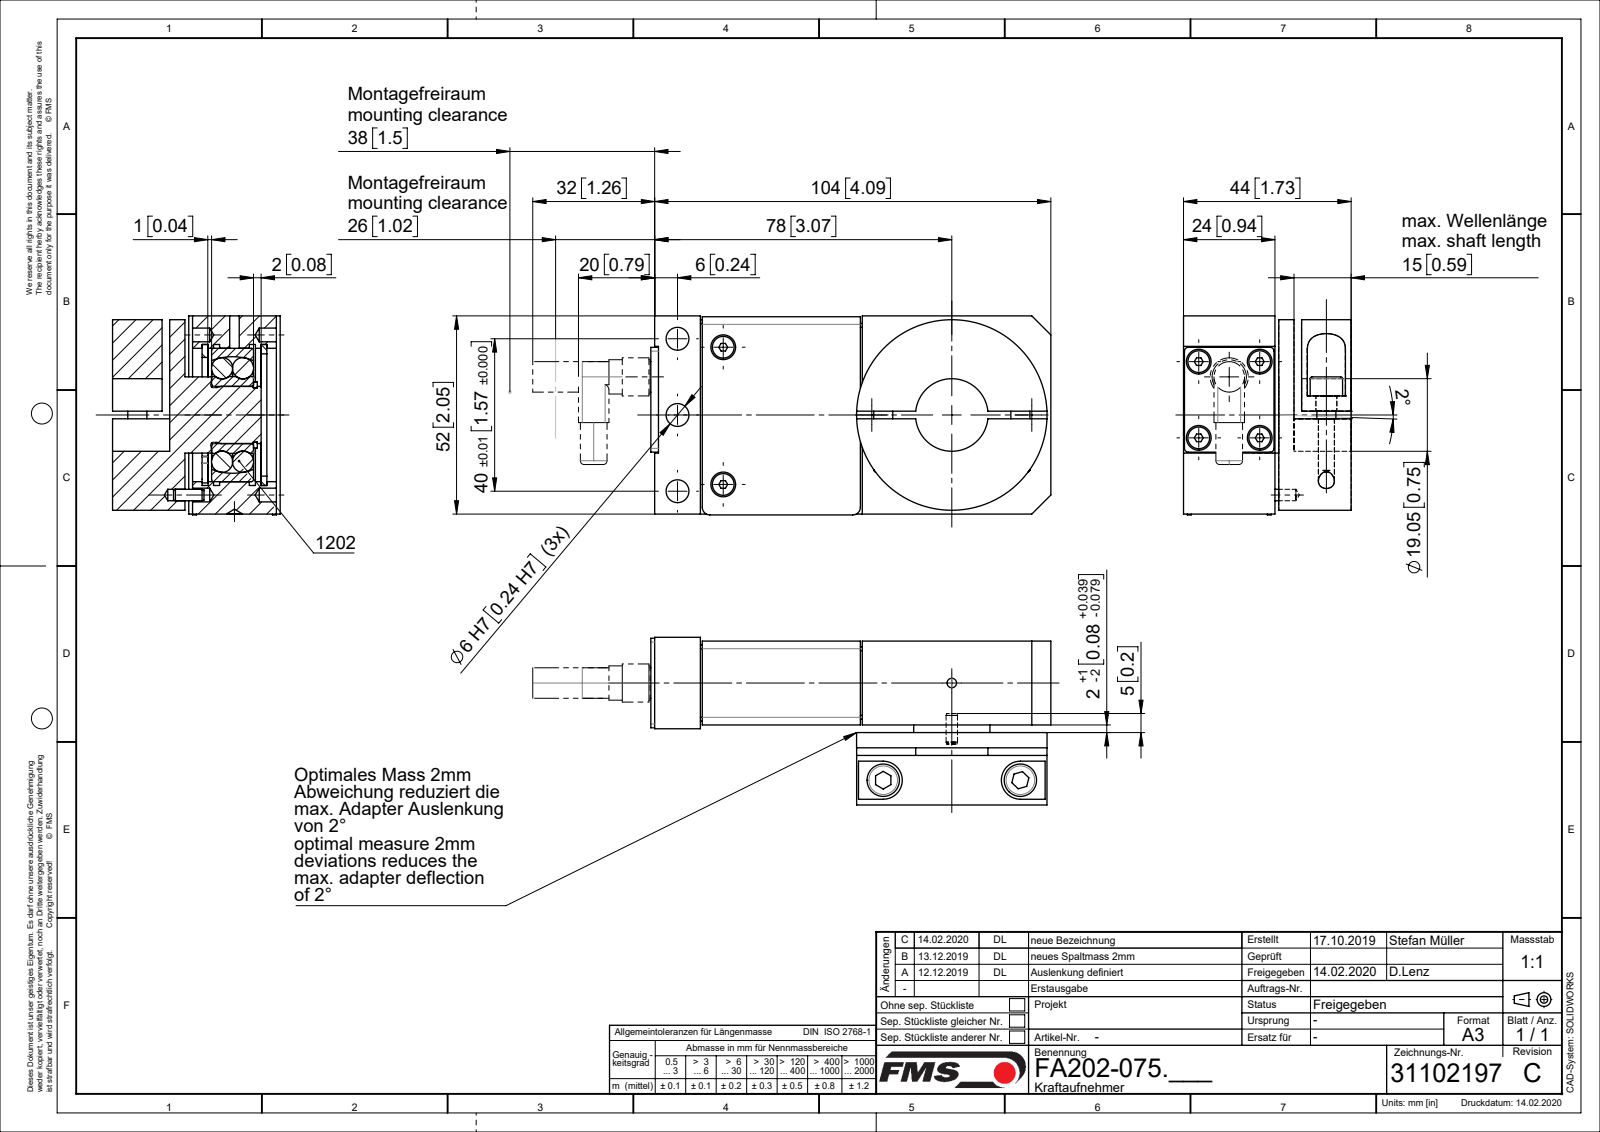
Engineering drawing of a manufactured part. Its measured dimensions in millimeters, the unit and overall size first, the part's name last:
Units: millimetres
Overall size (bounding box): 123 × 52 × 50
Round holes (diameter × count): ⌀2.6 ×7, ⌀1 ×4, ⌀3.2 ×4, ⌀3.6 ×4, ⌀6 ×4, ⌀4.33 ×2, ⌀5.5 ×2, ⌀3 ×1, ⌀4 ×1, ⌀6.5 ×1, ⌀7 ×1, ⌀14.3 ×1
Round bosses / shafts (diameter × count): ⌀6 ×7, ⌀3 ×6, ⌀1 ×4, ⌀8 ×3, ⌀10 ×2, ⌀5 ×2, ⌀50 ×1, ⌀22.6 ×1
Partial cylindrical surfaces — rounded edges, fillets, slot ends (radius × count): R2 ×8, R1 ×6, R5 ×2, R4.1 ×1
Main face-to-face distances: 1, 21, 22, 1.5, 2, 6, 19, 2.5, 18, 19.5
Hole centre spacings: 2.24, 20, 21, 29.7, 2, 10, 3.61, 7.21
Volume: 139 276 mm³ · Surface area: 59 202 mm²
Bodies: 26 solids, 606 faces (229 planar, 221 cylindrical, 156 other)
Part name (STEP PRODUCT): F0807306C_DI075; F0807304; F0807305; SENKSCHRAUBE_I-6KT_M3X6 (+8 more)
STEP written by: Mechanical Desktop 2009 (CONFIG_CONTROL_DESIGN)
